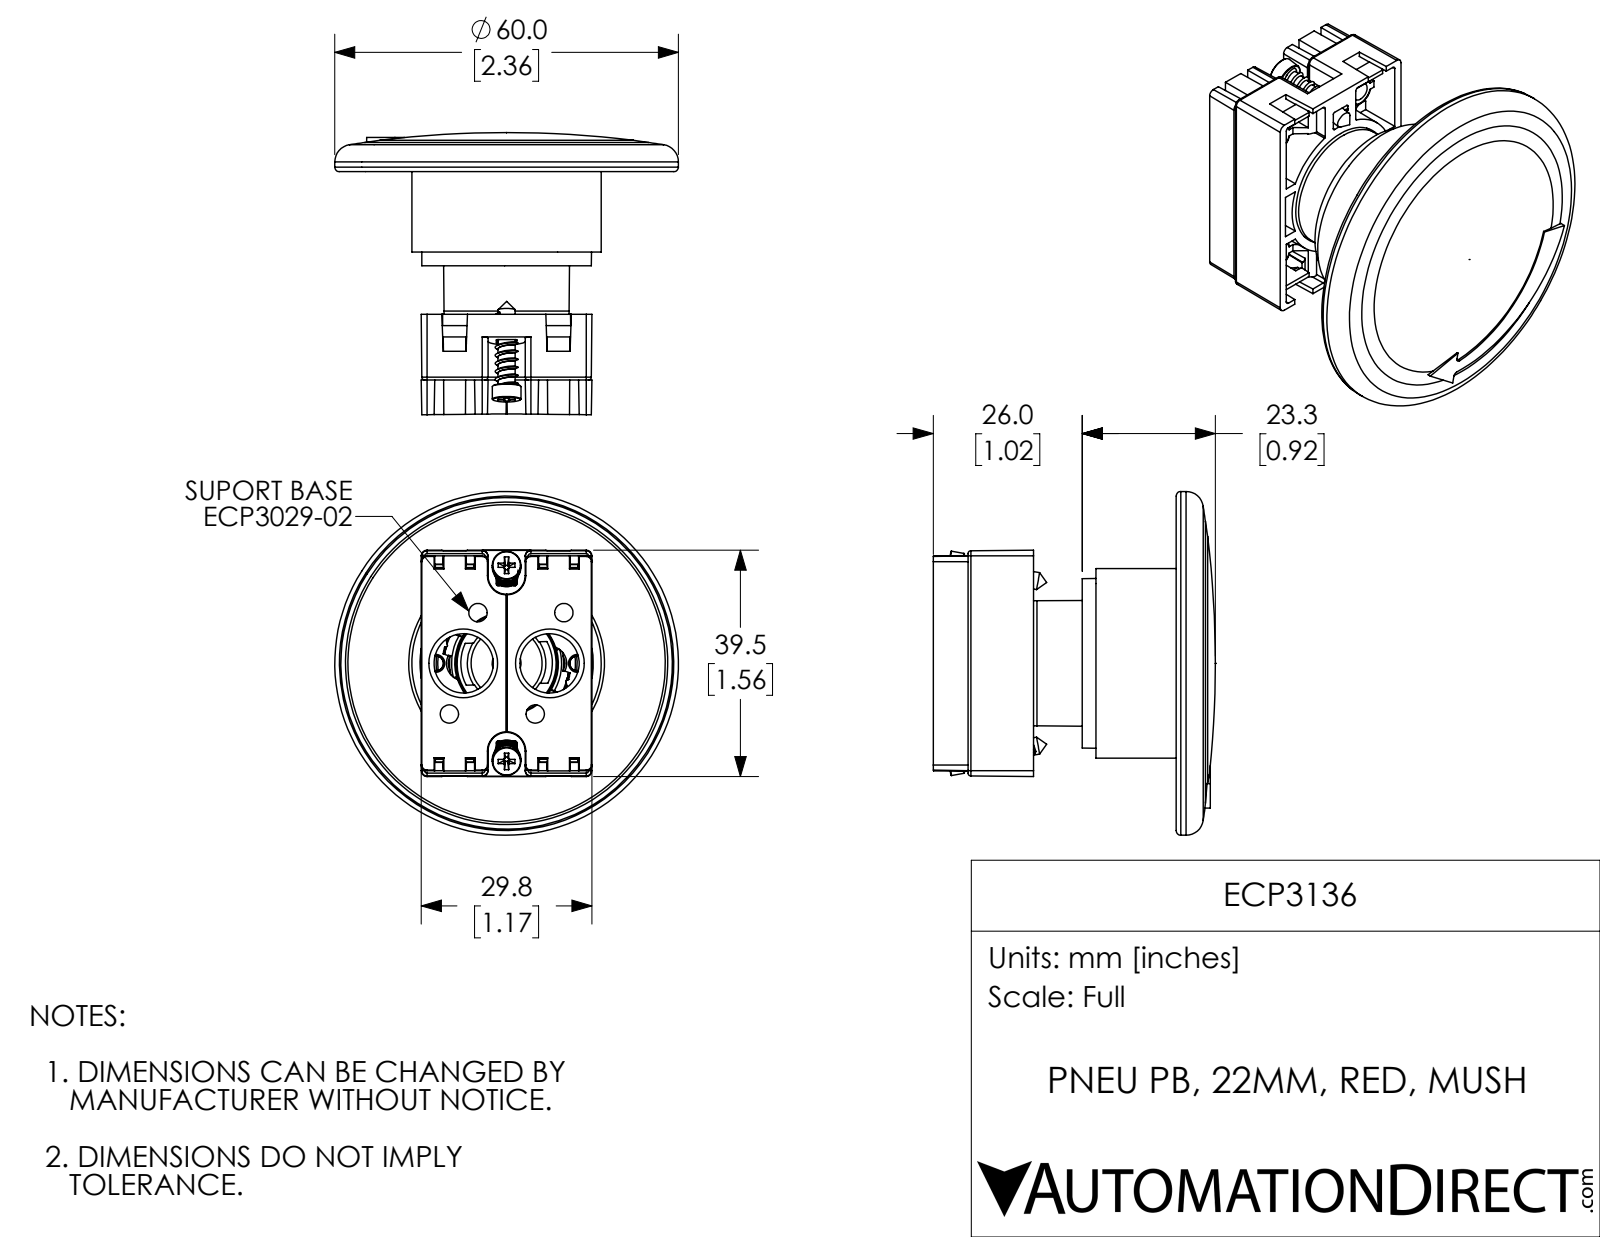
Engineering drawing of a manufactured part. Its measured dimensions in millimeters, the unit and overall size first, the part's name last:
Units: millimetres
Overall size (bounding box): 60 × 60 × 49.3
Round holes (diameter × count): ⌀2.1 ×4, ⌀10.3 ×2, ⌀2.6 ×1, ⌀3 ×1, ⌀17.7 ×1, ⌀19.2 ×1, ⌀22.7 ×1, ⌀30.3 ×1, ⌀56.3 ×1
Round bosses / shafts (diameter × count): ⌀5 ×2, ⌀3 ×2, ⌀60 ×1, ⌀33.1 ×1, ⌀21.8 ×1, ⌀19.2 ×1, ⌀13.7 ×1, ⌀12.4 ×1
Partial cylindrical surfaces — rounded edges, fillets, slot ends (radius × count): R0.5 ×18, R0.2 ×8, R0.3 ×8, R0.2 ×4, R1 ×4, R0.2 ×2, R0.6 ×2, R3 ×2
Main face-to-face distances: 30.3, 1.7, 18.2, 18.8, 11.5, 14.9, 13.2, 34.8, 16, 4.5
Hole centre spacings: 7.7, 13.7, 20.8, 7.5, 12, 24.7, 27.5, 15
Volume: 30 480 mm³ · Surface area: 28 070 mm²
Bodies: 7 solids, 830 faces (374 planar, 157 cylindrical, 299 other)
Part name (STEP PRODUCT): ECP3136
STEP written by: SolidWorks 2017 (AUTOMOTIVE_DESIGN)
